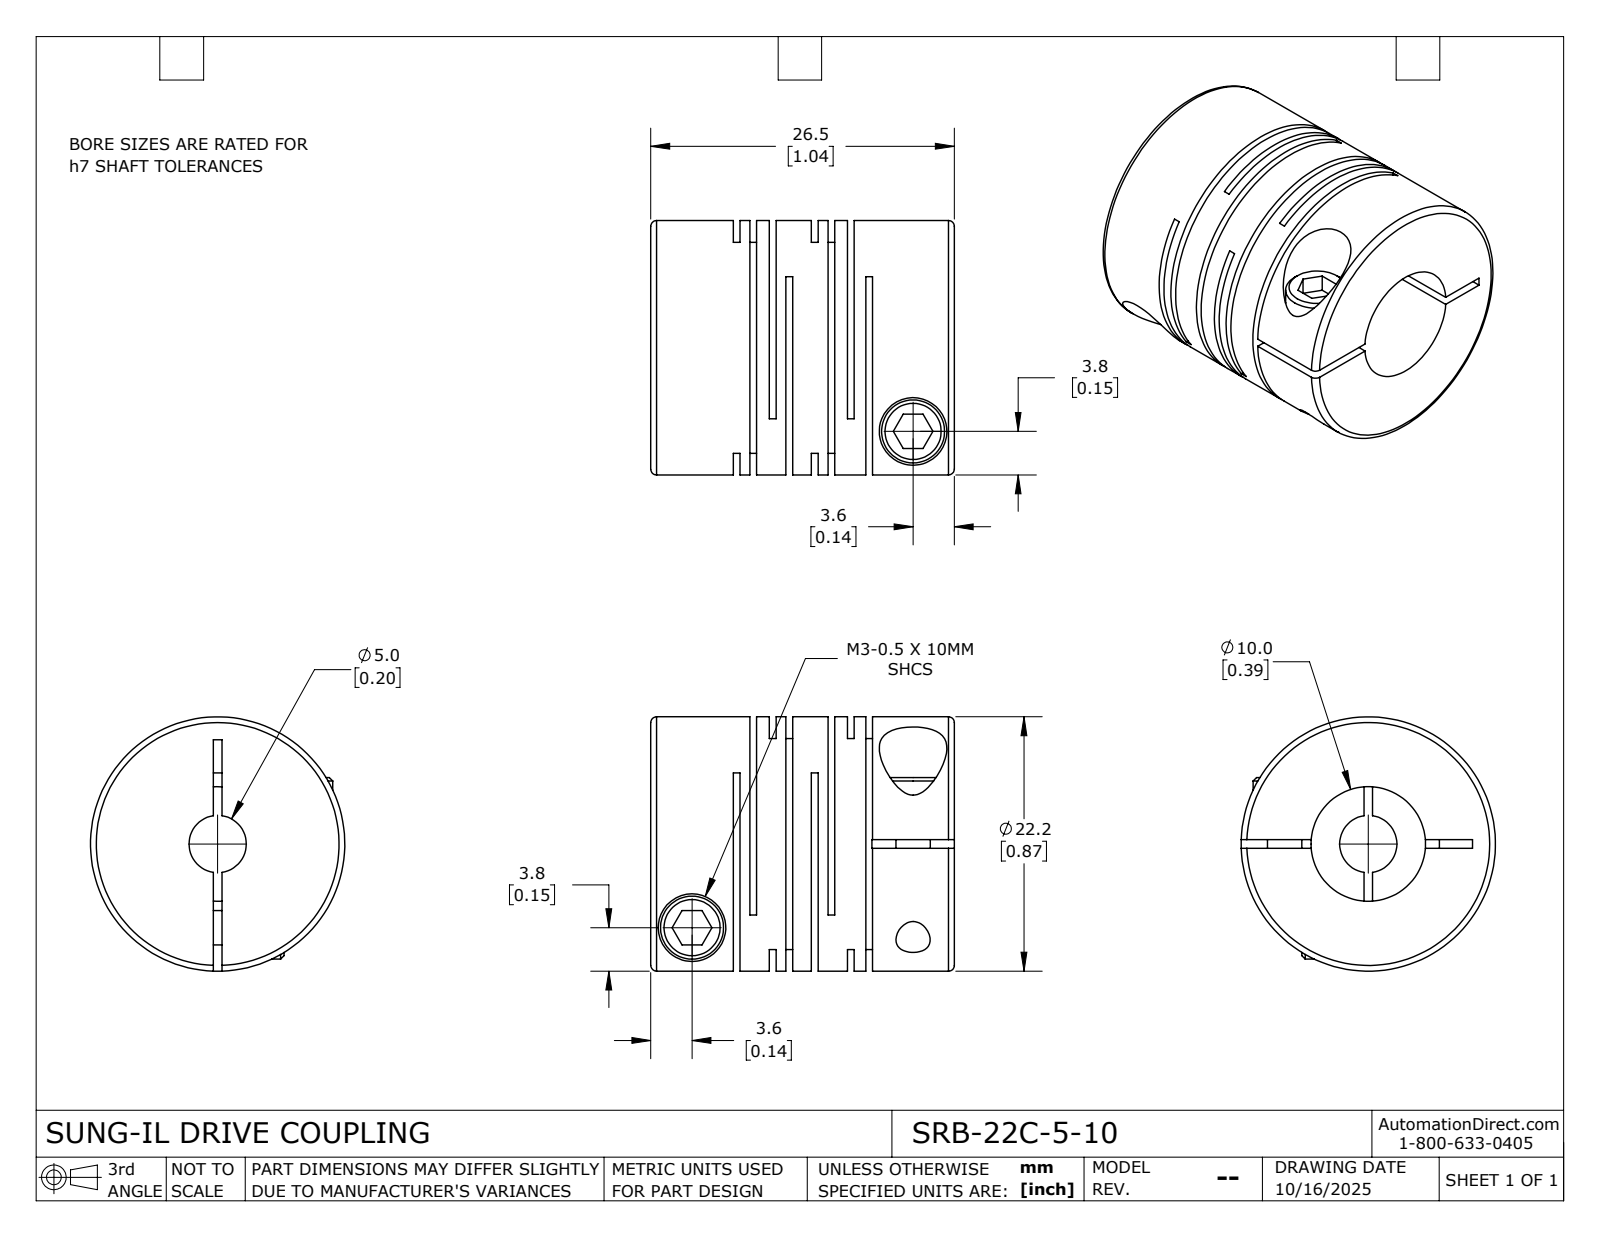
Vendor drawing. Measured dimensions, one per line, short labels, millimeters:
name: SRB-22C-5-10
written by: SolidWorks 2024 (CONFIG_CONTROL_DESIGN)
unit: mm
bodies: 1 solid, 115 faces (60 planar, 42 cylindrical, 13 other)
size: 26.5 × 22.2 × 22.2
volume: 7 119 mm³; area: 7 487 mm²
holes: 2× ⌀3, 2× ⌀5.9, 1× ⌀5, 1× ⌀10
bosses: 2× ⌀5.5, 1× ⌀22.2
face distances: 0.59, 3.15, 6.82, 1.45, 5.37, 3.67, 1.7, 2.04, 3.74, 7.41
